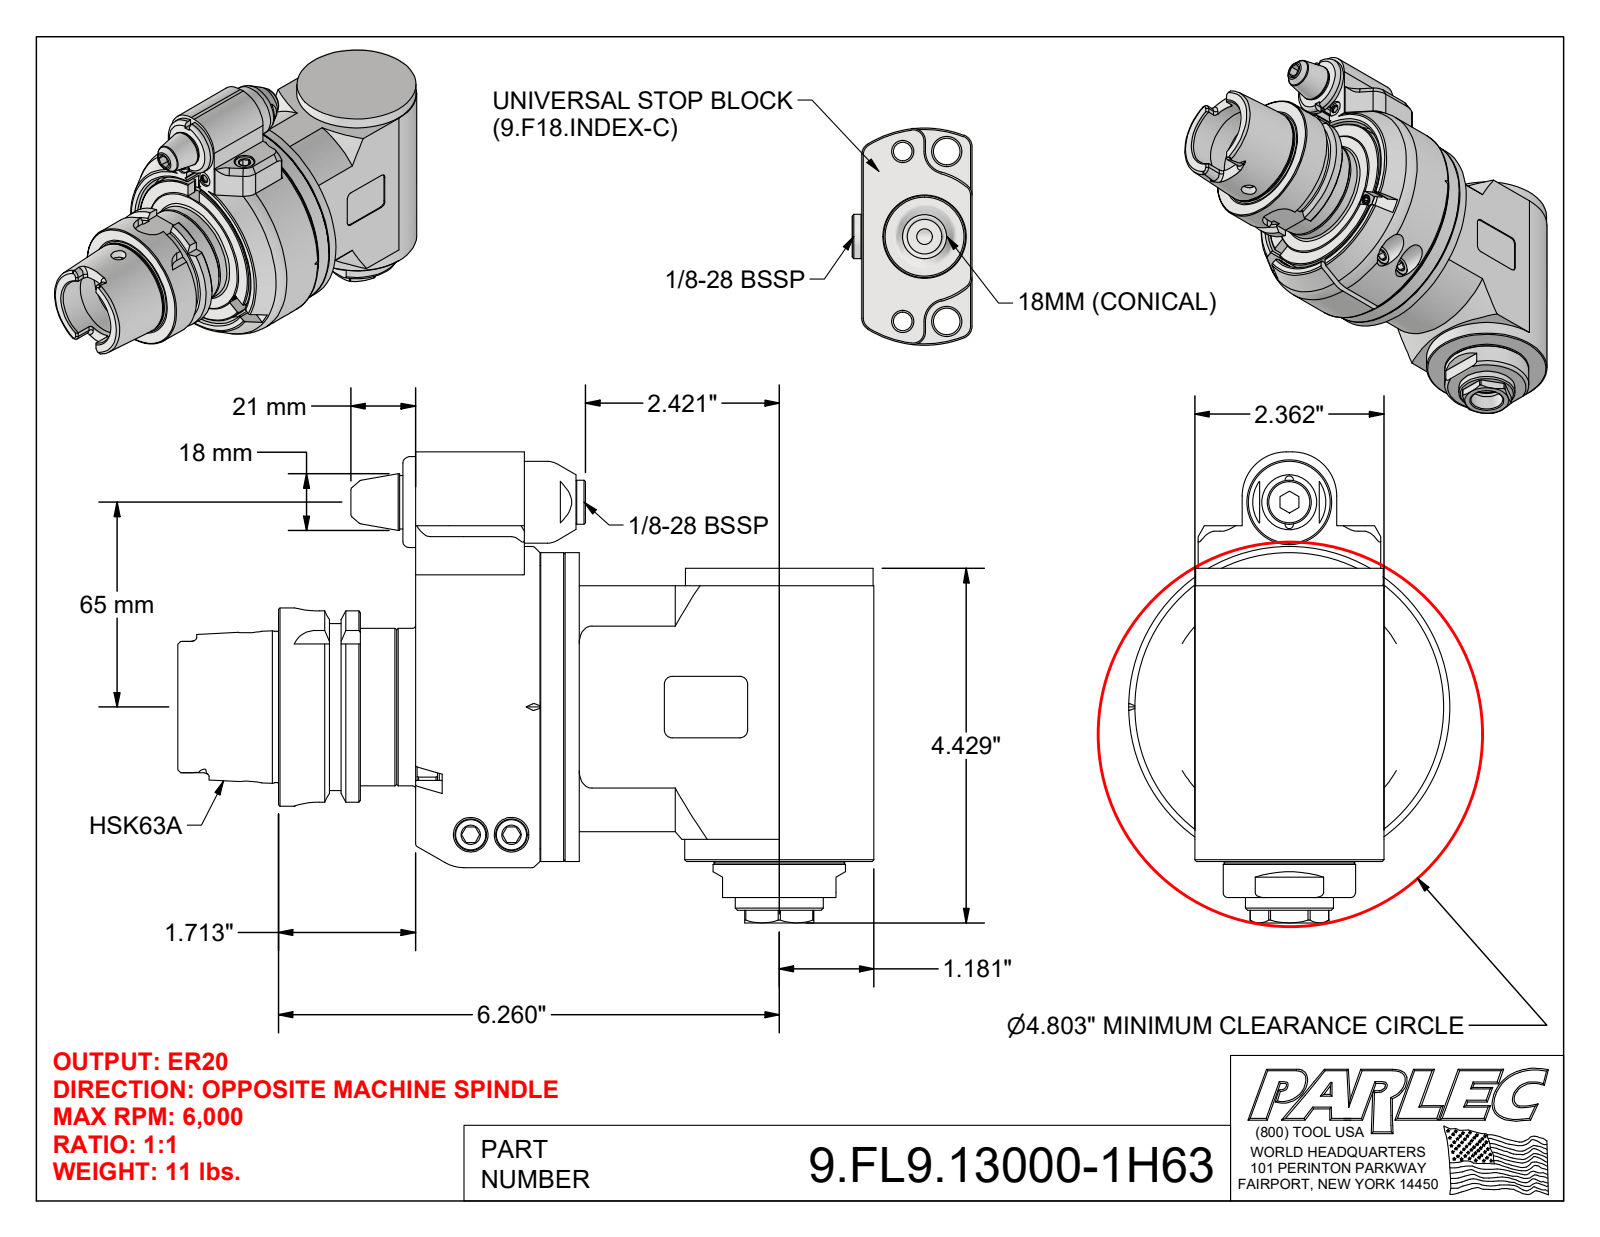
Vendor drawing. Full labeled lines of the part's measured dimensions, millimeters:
Part name (STEP PRODUCT): 9.FL9.13000-1H63; 9_FL9_13000; 9GA15C_566 (Type 1, H63A, 65mm, Conical)
STEP written by: Autodesk Inventor 2022 (AUTOMOTIVE_DESIGN)
Units: millimetres
Bodies: 4 solids, 597 faces (287 planar, 158 cylindrical, 152 other)
Overall size (bounding box): 221 × 149.5 × 102
Volume: 883 900 mm³ · Surface area: 133 000 mm²
Round holes (diameter × count): ⌀5 ×3, ⌀2.6 ×2, ⌀3.3 ×2, ⌀4.2 ×2, ⌀6.5 ×2, ⌀8 ×2, ⌀10.4 ×2, ⌀11 ×2, ⌀29 ×2, ⌀2.5 ×1, ⌀3 ×1, ⌀6 ×1
Round bosses / shafts (diameter × count): ⌀10 ×5, ⌀18 ×2, ⌀8 ×2, ⌀6 ×2, ⌀102 ×1, ⌀98 ×1, ⌀90 ×1, ⌀77 ×1
Partial cylindrical surfaces — rounded edges, fillets, slot ends (radius × count): R1 ×14, R1.5 ×6, R3 ×6, R8 ×6, R2.5 ×4, R2.9 ×4, R4 ×4, R0.5 ×2
Main face-to-face distances: 60, 0.5, 7, 43.5, 52, 12.5, 32, 26, 31, 1
Hole centre spacings: 7, 12.8, 18.8, 25.3, 48.7, 168, 1.2, 13
